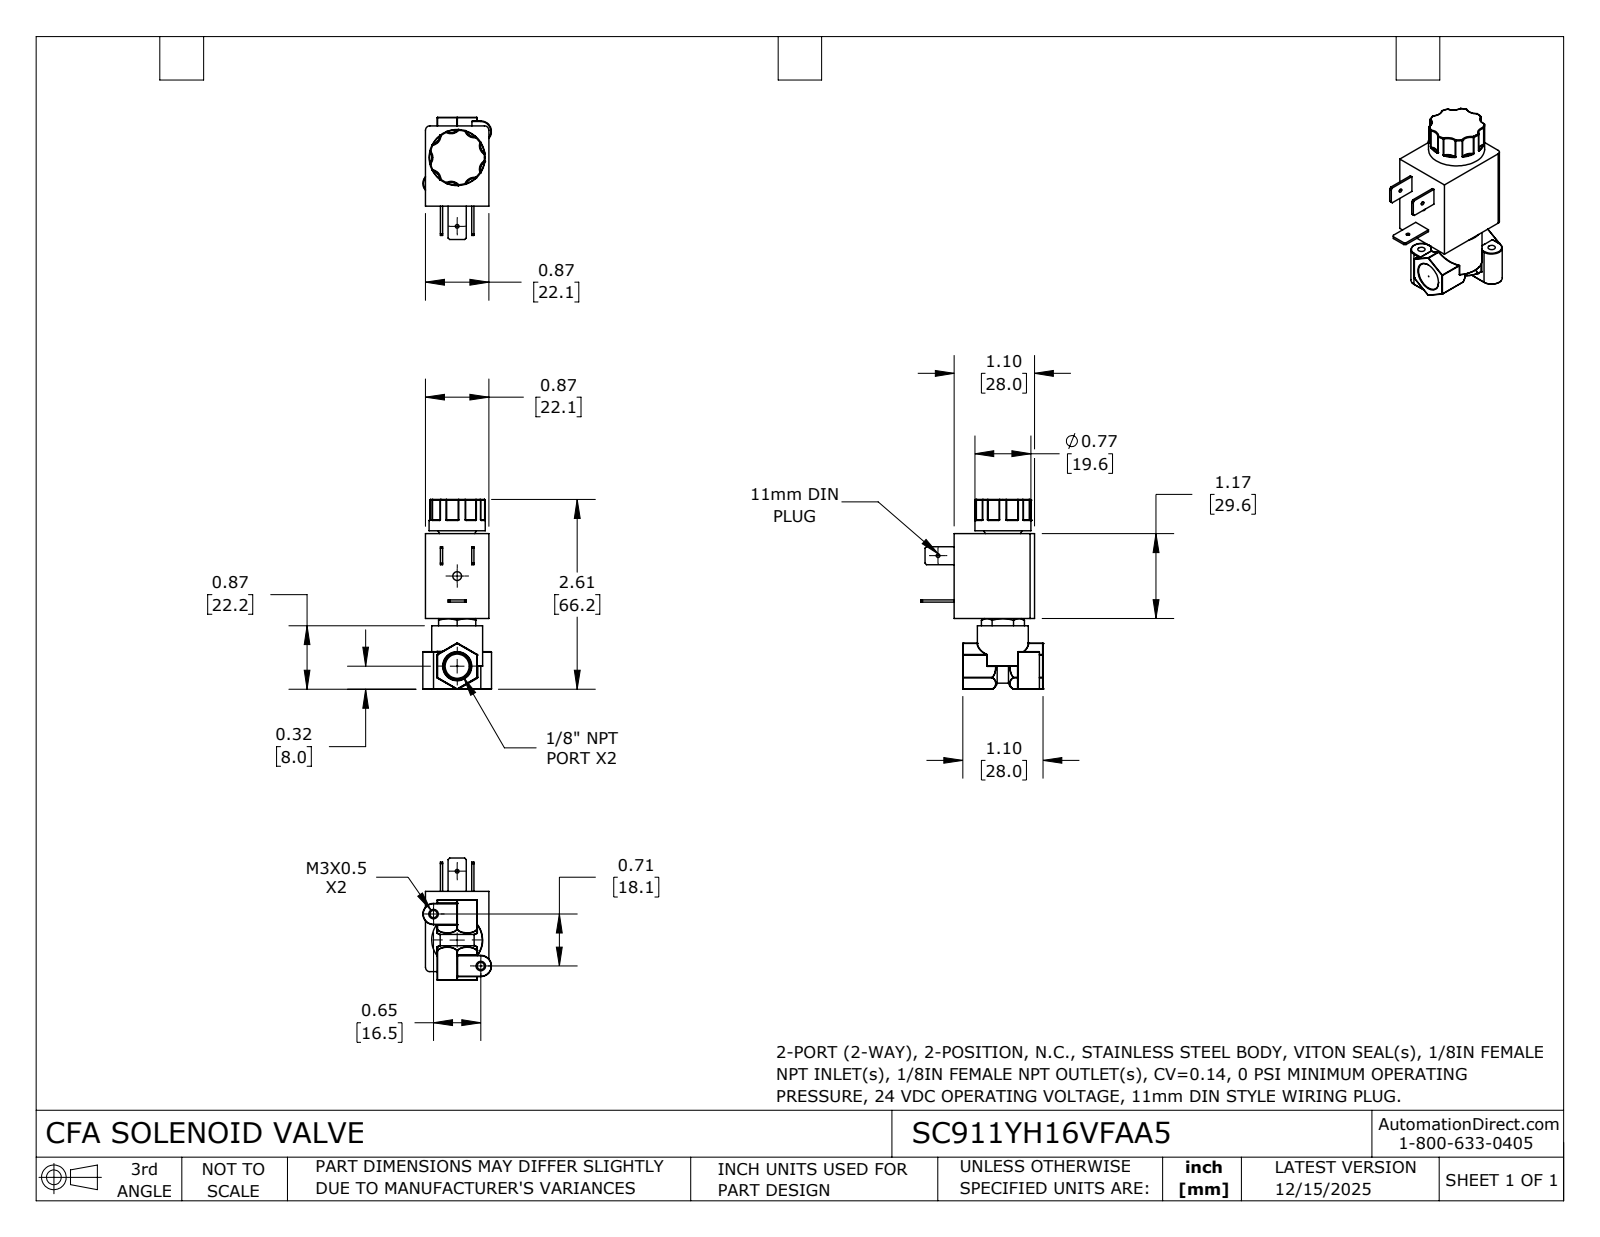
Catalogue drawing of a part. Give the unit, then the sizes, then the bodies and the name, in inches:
Units: inches
Overall size (bounding box): 2.608 × 1.678 × 0.942
Round holes (diameter × count): ⌀0.05 ×2, ⌀0.1 ×2, ⌀0.12 ×1
Round bosses / shafts (diameter × count): ⌀0.77 ×1, ⌀0.7 ×1, ⌀0.332 ×1
Partial cylindrical surfaces — rounded edges, fillets, slot ends (radius × count): R0.004 ×27, R0.01 ×18, R0.008 ×12, R0.133 ×7, R0.017 ×2, R0.06 ×2, R0.132 ×2, R0.146 ×2
Main face-to-face distances: 0.87, 1.104, 1.167, 1.637, 0.47, 0.548, 0.161, 0.709, 1.207, 0.04
Hole centre spacings: 0.672, 0.965, 1.342
Volume: 1.713 in³ · Surface area: 14.37 in²
Bodies: 1 solid, 393 faces (76 planar, 108 cylindrical, 209 other)
Part name (STEP PRODUCT): SC911YH16VFAA5
STEP written by: SolidWorks 2024 (CONFIG_CONTROL_DESIGN)
